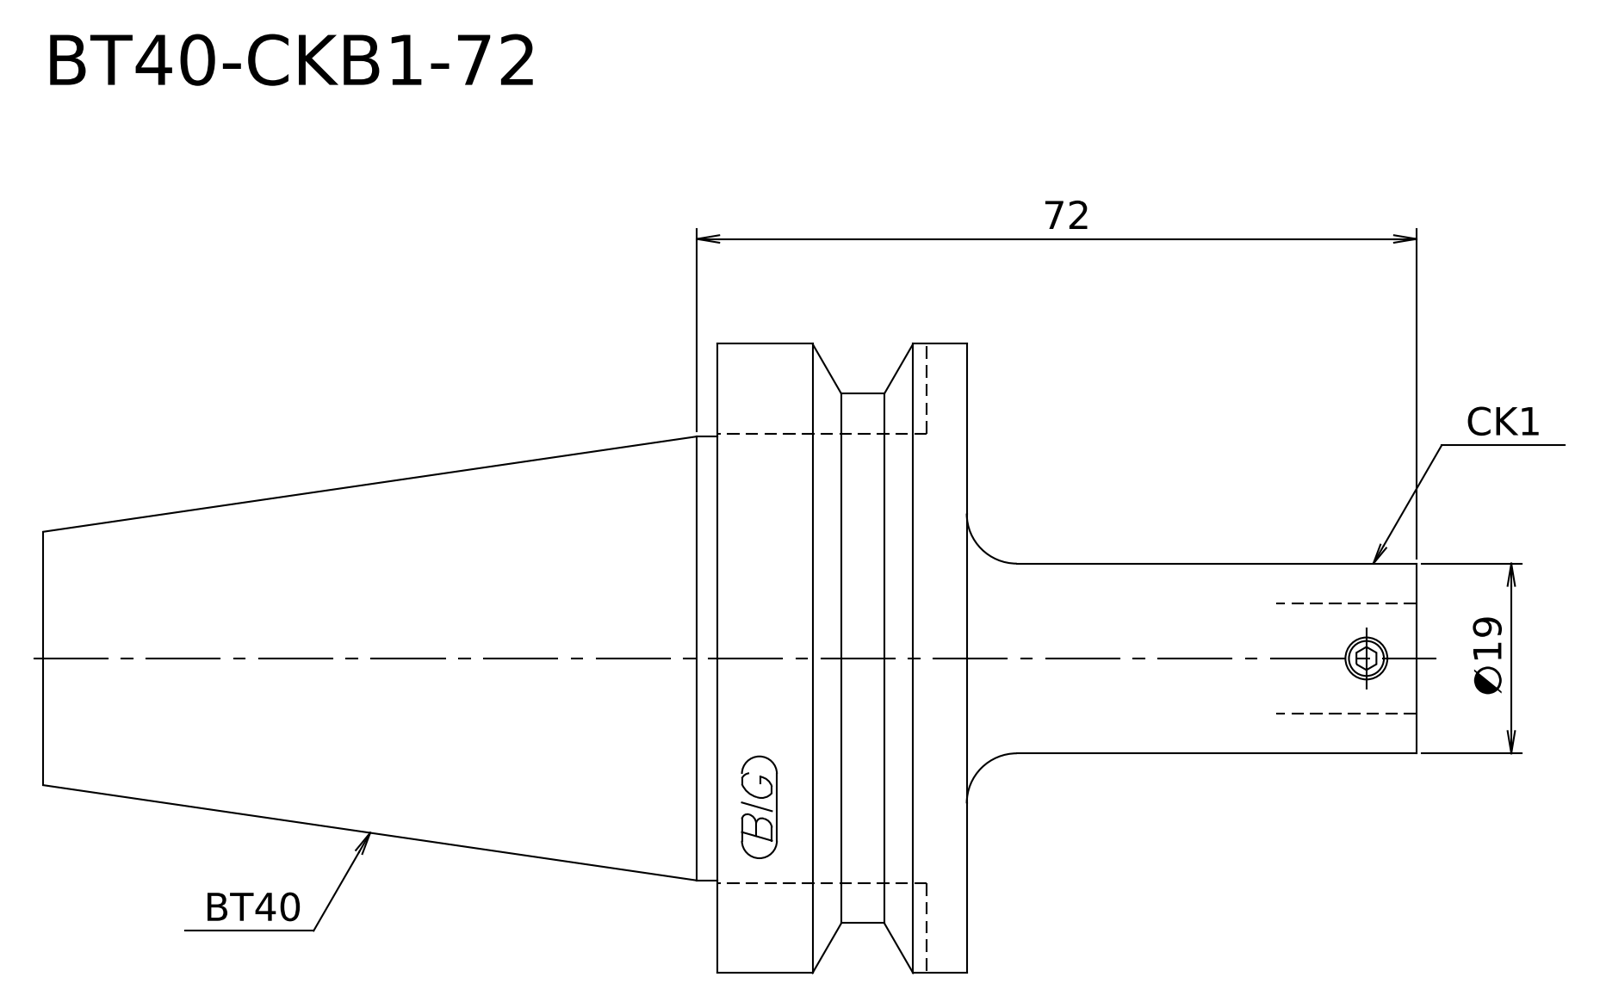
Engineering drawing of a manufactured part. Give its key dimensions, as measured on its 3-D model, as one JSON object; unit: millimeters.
{"step_written_by": "Kubotek KeyCreator V8.5.1 (14335) (CONFIG_CONTROL_DESIGN)", "units": "millimeters", "bodies": {"solids": 1, "faces": 14, "planar": 4, "cylindrical": 5, "other": 5}, "overall_size": [137.4, 63, 63], "volume_mm3": 152272, "surface_area_mm2": 21019, "round_bosses_or_shafts": [[63, 1], [53, 1], [44.45, 1], [19, 1]], "face_to_face_distances": [25, 92.4, 67.4, 45, 70, 137.4]}
